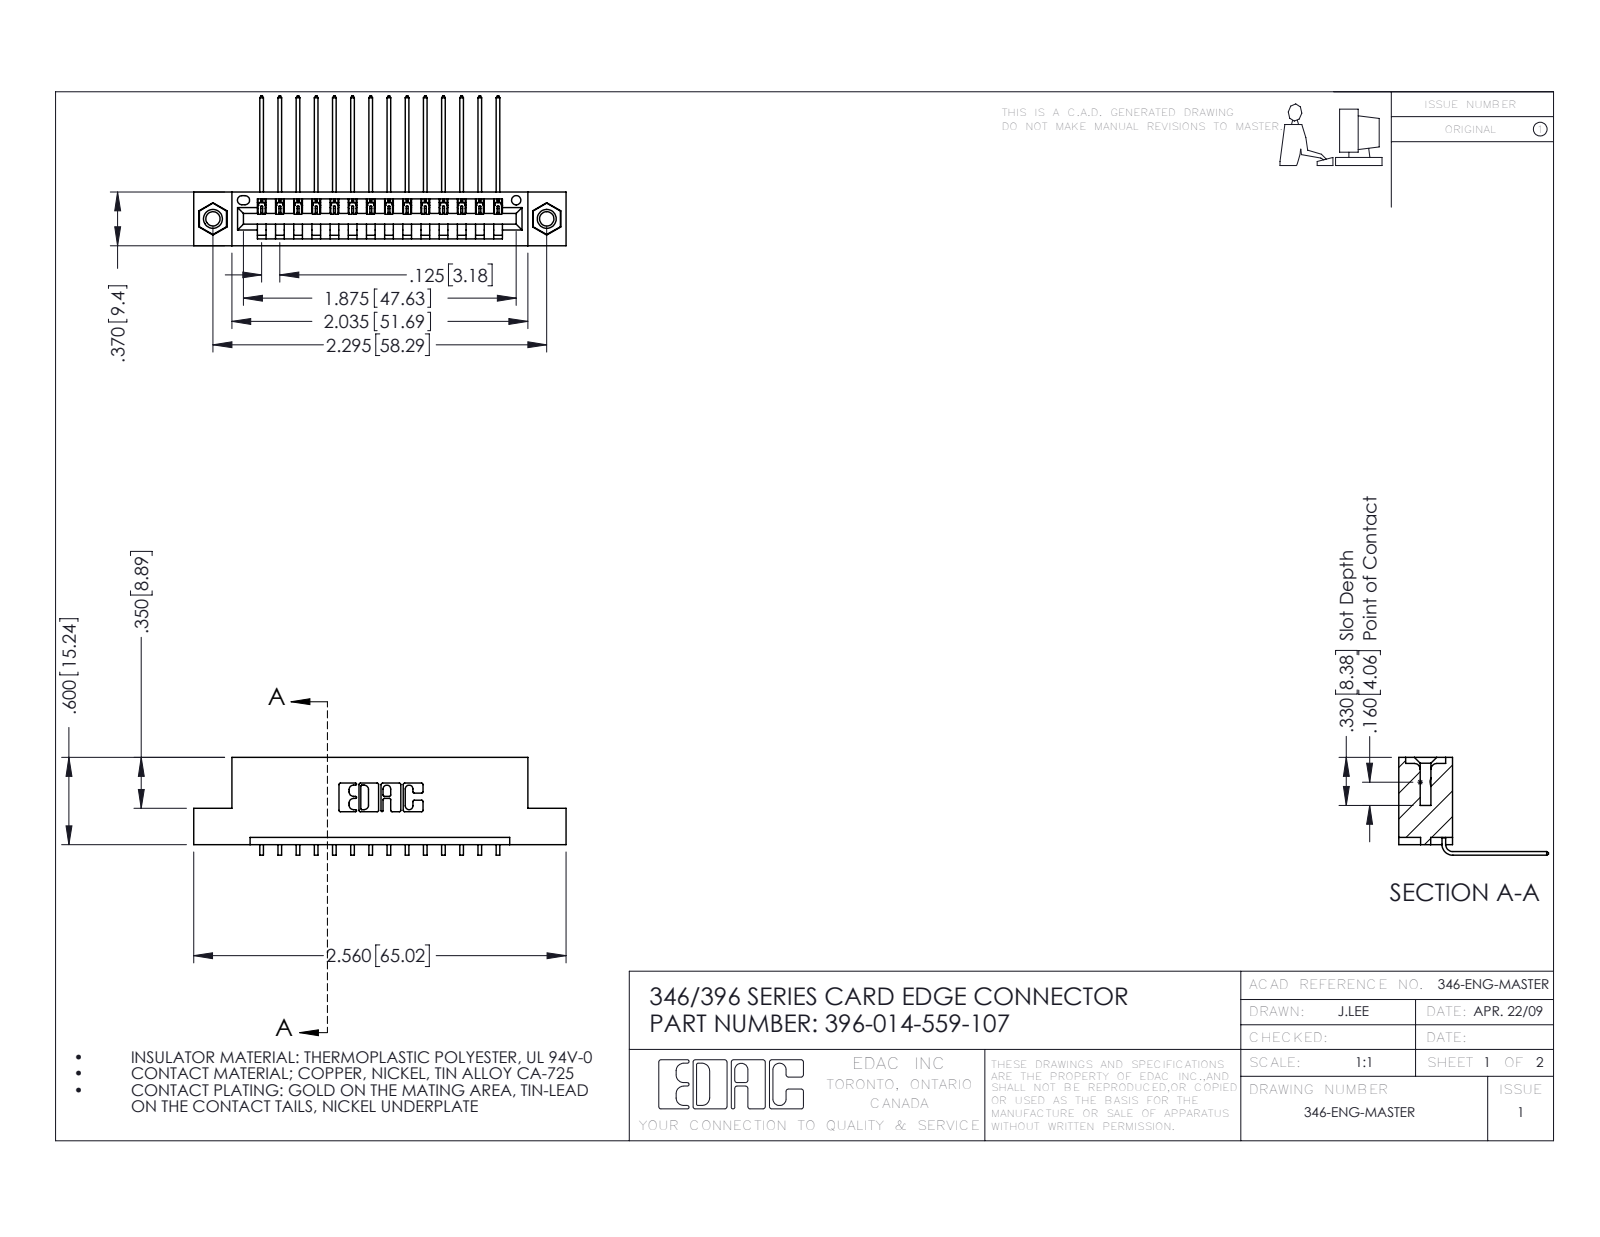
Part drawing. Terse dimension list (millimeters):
name: 345-250-001_345-250-005-103; 396-014-559-107; 345-292-001_558 559 Tail - 1; 346 Part_Flush Mounting Lugs - 0.156 Dia-TI
written by: SolidWorks 2016 (CONFIG_CONTROL_DESIGN)
unit: mm
bodies: 17 solids, 1022 faces (696 planar, 310 cylindrical, 16 other)
size: 65 × 26.2 × 17.1
volume: 6 060 mm³; area: 7 594 mm²
holes: 2× ⌀2.5, 2× ⌀3.2, 2× ⌀4, 1× ⌀1.6
bosses: 2× ⌀3.9
rounds: 28× R0.2, 22× R0.3, 6× R0.2, 6× R0.8, 3× R0.7, 2× R0.8, 2× R1, 1× R0.4
face distances: 1.2, 8.2, 6.4, 9.4, 1.8, 0.6, 7.6, 3.8, 5.6, 2.5
hole spacings: 6.2, 53.1, 58.3
